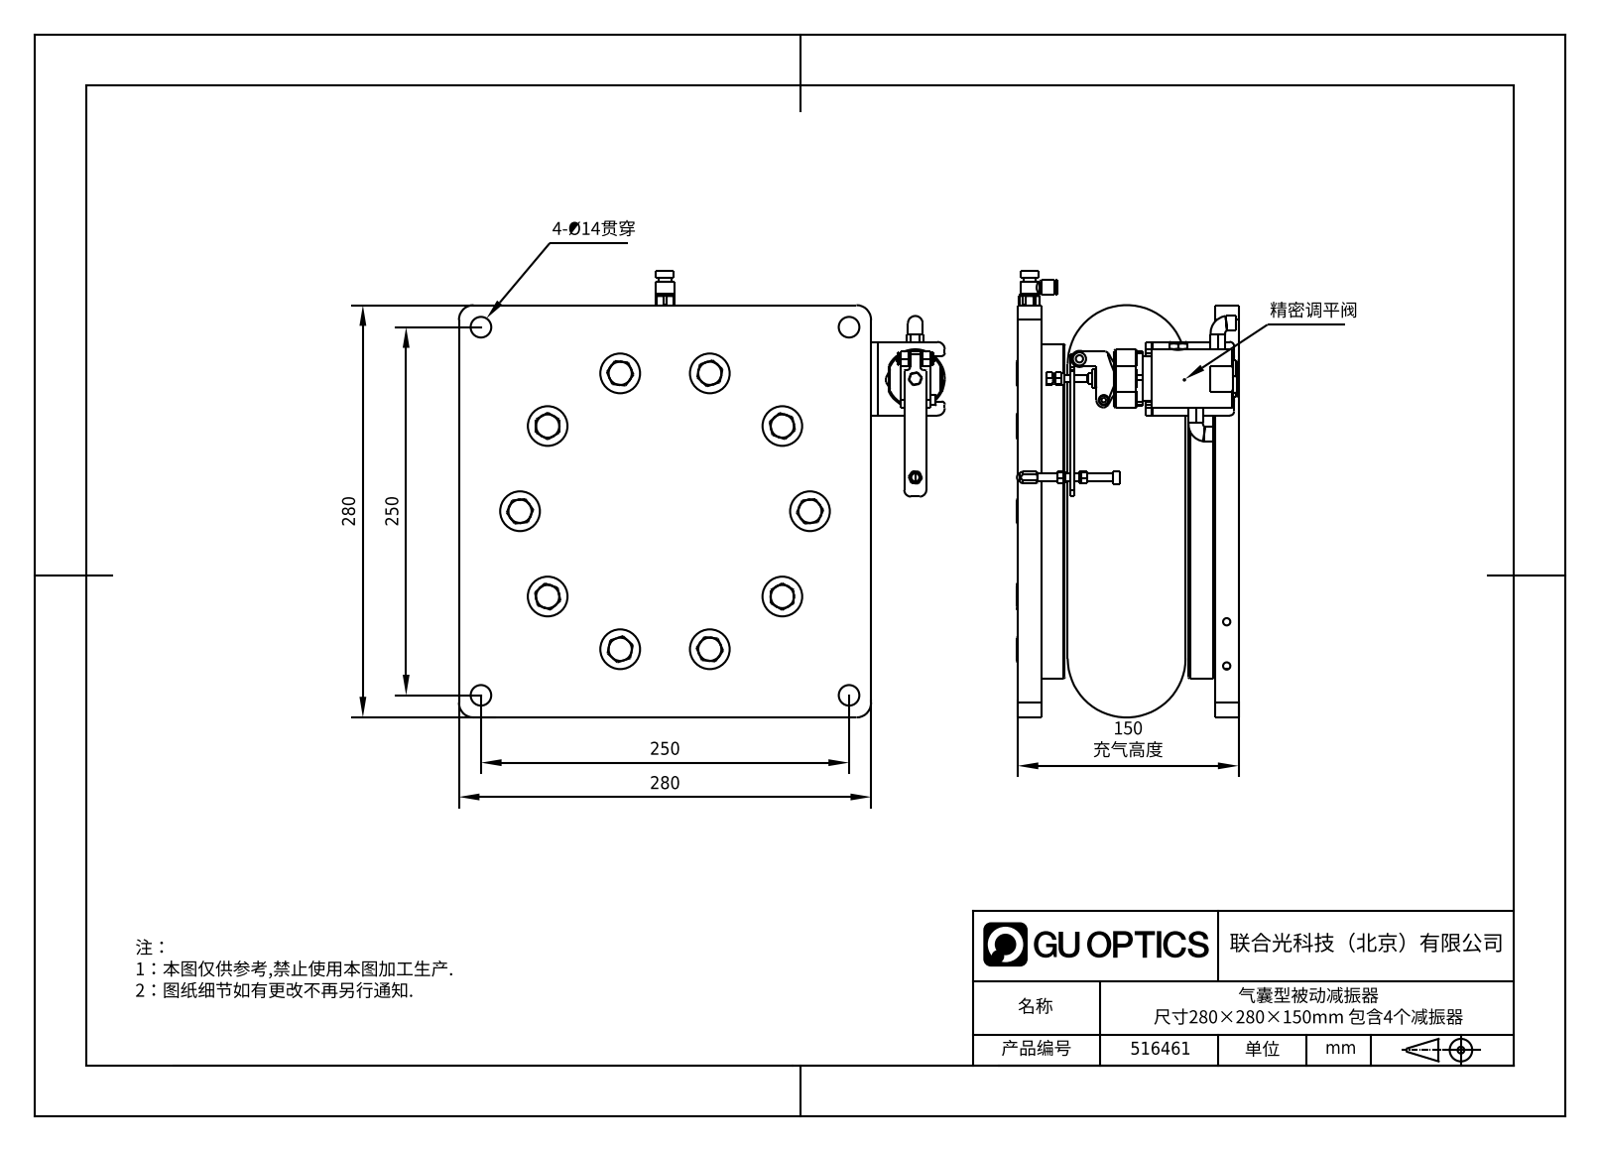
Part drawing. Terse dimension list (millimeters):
name: 516461
written by: SolidWorks 2020 (AUTOMOTIVE_DESIGN)
unit: mm
bodies: 0 solids, 623 faces (344 planar, 120 cylindrical, 159 other)
size: 330 × 303.5 × 150.67
holes: 10× ⌀27, 4× ⌀14, 3× ⌀5, 2× ⌀16.1, 1× ⌀9.7, 1× ⌀11.5, 1× ⌀13, 1× ⌀40, 1× ⌀227
bosses: 4× ⌀10, 3× ⌀8, 2× ⌀7, 2× ⌀5, 1× ⌀30, 1× ⌀12.7, 1× ⌀12.6, 1× ⌀12
rounds: 6× R5, 5× R0.3, 4× R10, 3× R2, 2× R3, 2× R4.5, 1× R0.74, 1× R4.74
face distances: 16, 134, 118, 150, 280, 4, 34, 18, 116, 100
hole spacings: 60.88, 98.5, 187.36, 115.79, 159.37, 80.97, 115.8, 127.78
